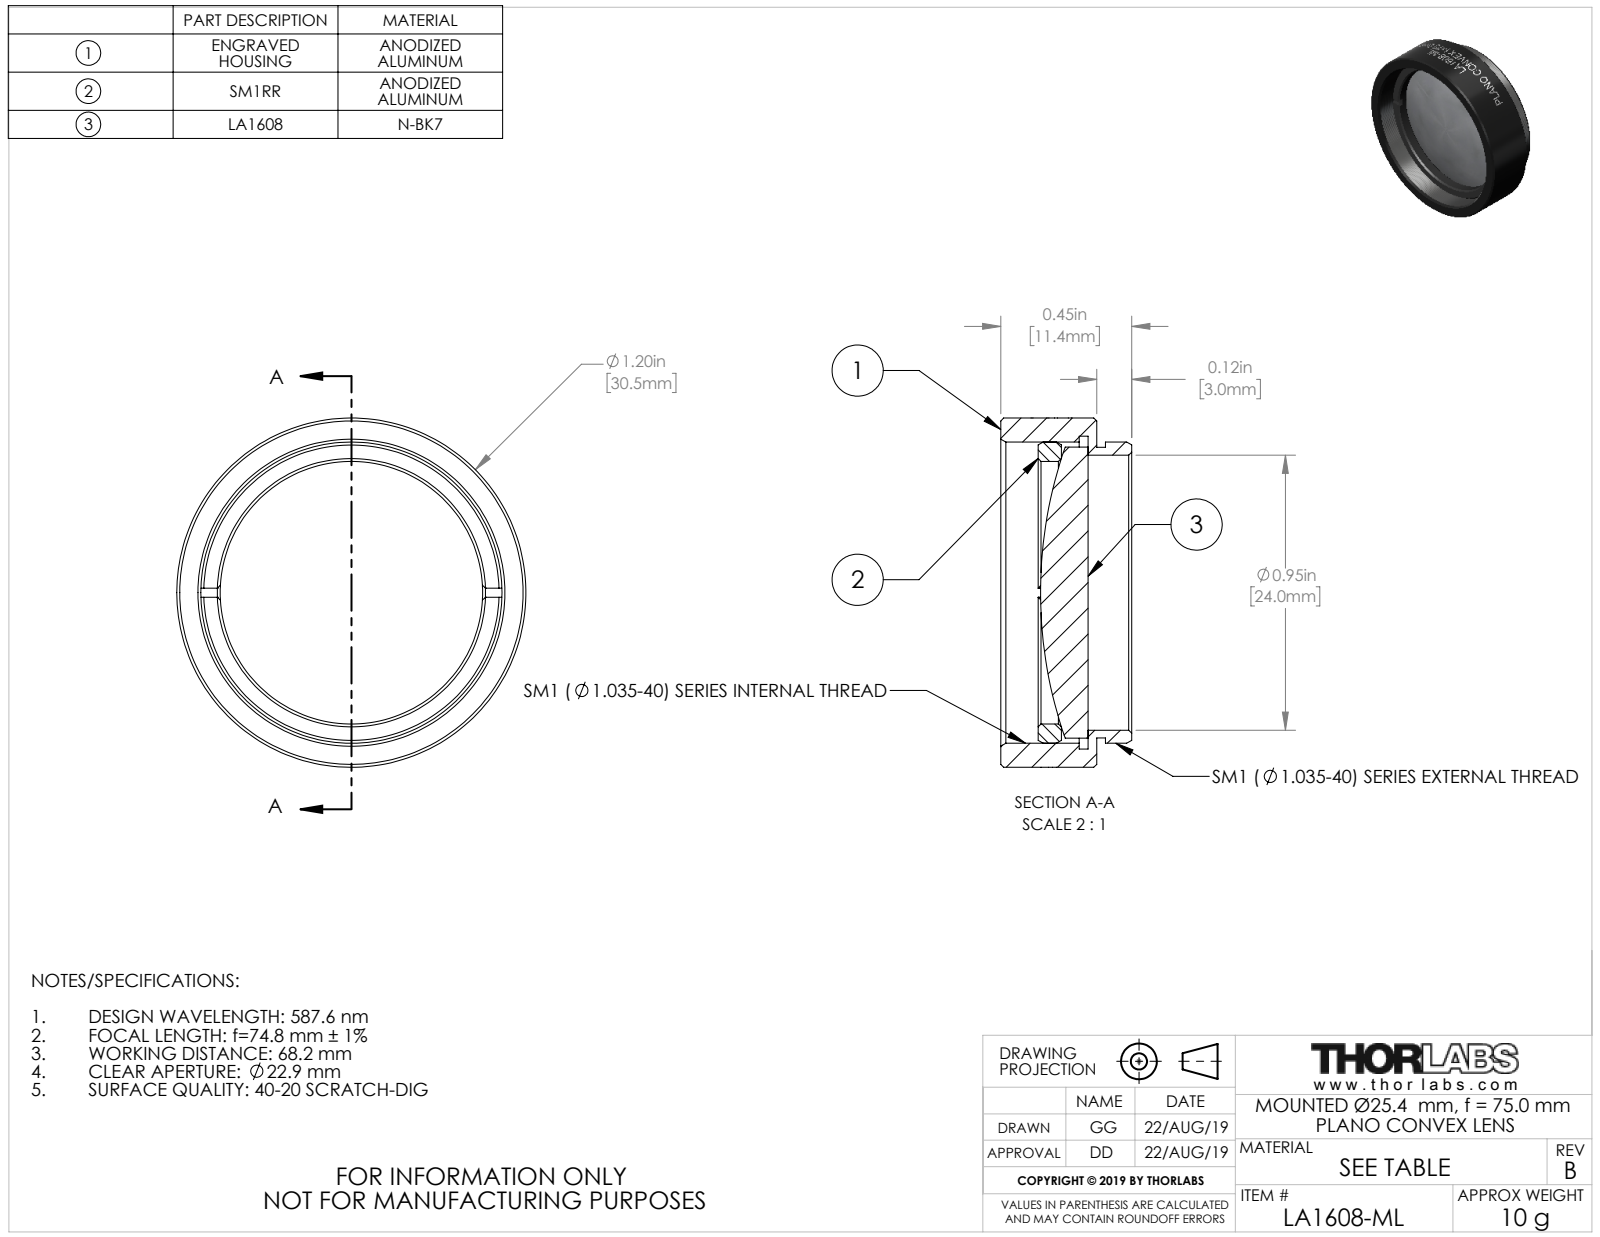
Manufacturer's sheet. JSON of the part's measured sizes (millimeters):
{"part_name": "24426-E0W", "step_written_by": "SolidWorks 2018 (CONFIG_CONTROL_DESIGN)", "units": "millimeters", "bodies": {"solids": 3, "faces": 118, "planar": 20, "cylindrical": 74, "other": 24}, "overall_size": [30.48, 30.48, 11.43], "volume_mm3": 3640, "surface_area_mm2": 4326, "round_holes": [[22.91, 1], [24, 1], [26.29, 1], [27.3, 1]], "round_bosses_or_shafts": [[30.48, 1], [26.29, 1], [25.4, 1], [25.37, 1]], "face_to_face_distances": [0.76, 8.38, 7.62, 3.08, 2.32, 5.3, 5.11, 4.35, 2.03, 3.27]}
